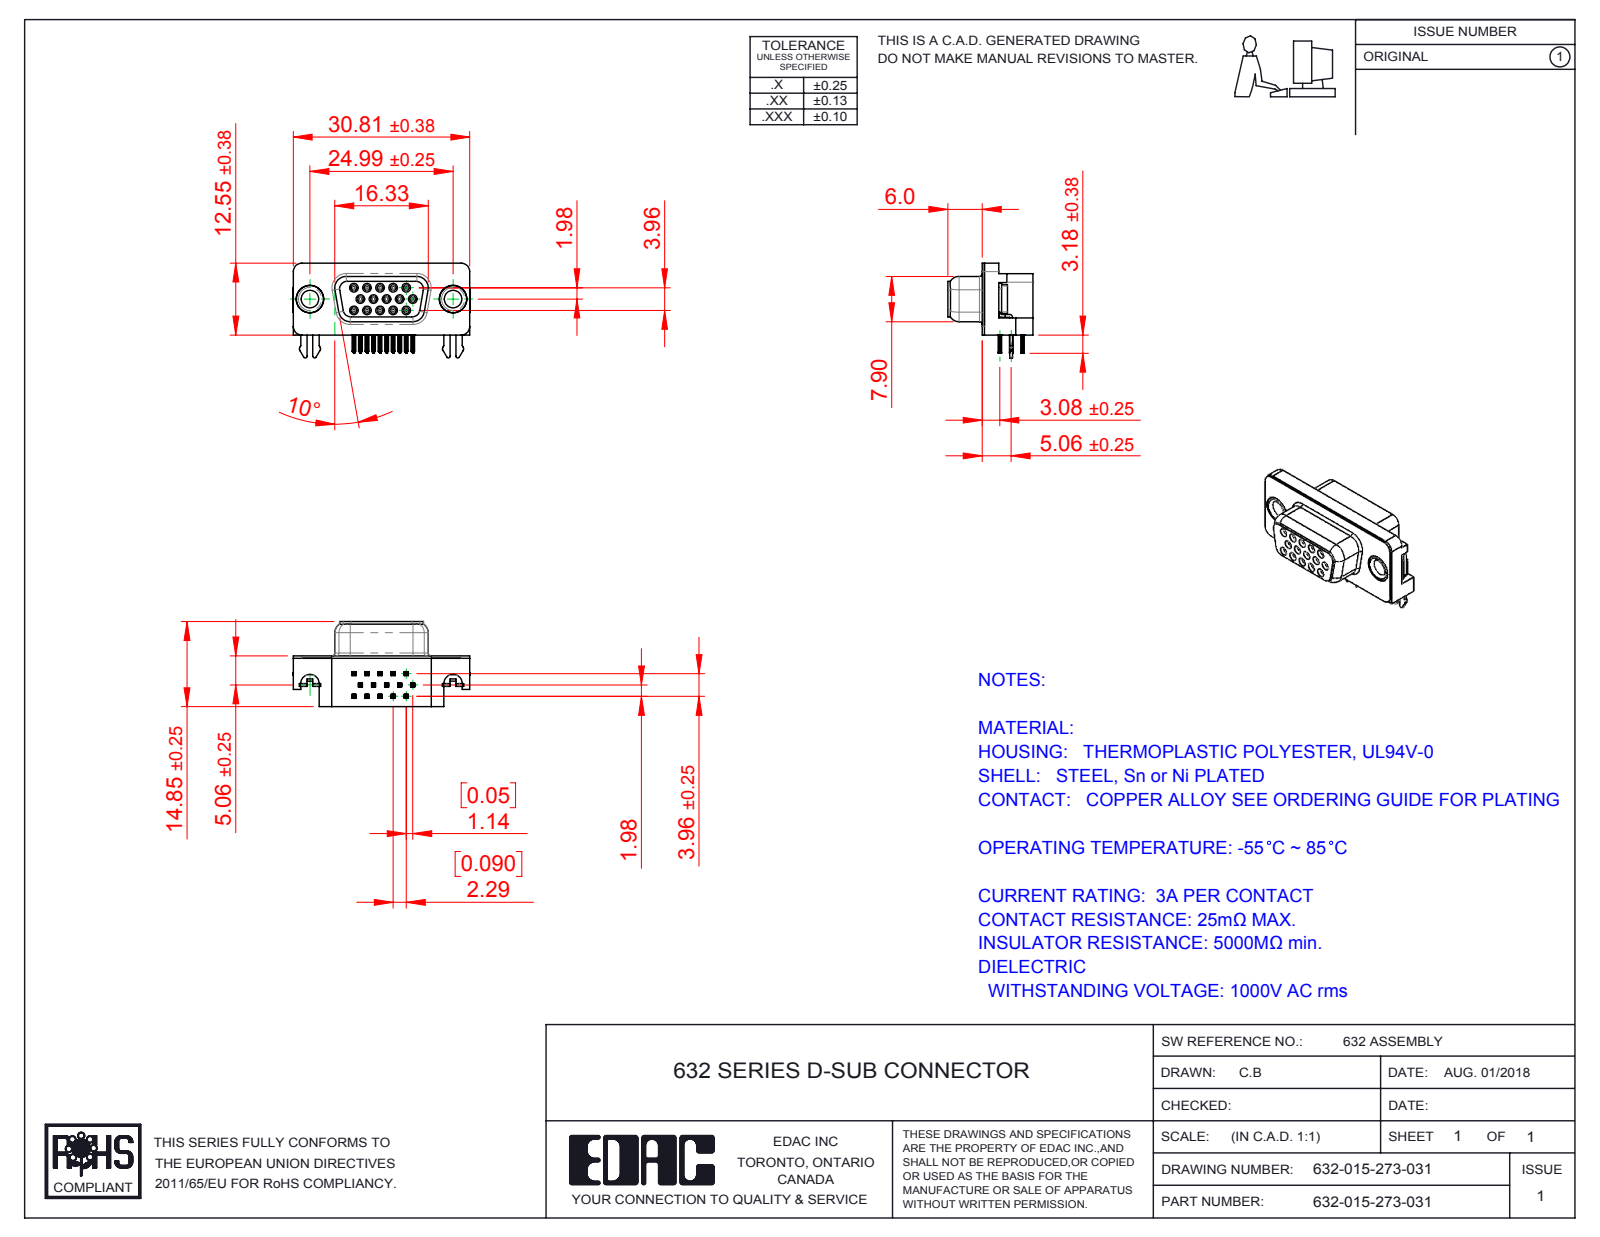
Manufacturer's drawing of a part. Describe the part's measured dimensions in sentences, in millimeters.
The part is named "632 Housing_15 Socket; 632 Shell_9 Socket; 632 Contact Middle; 632 2 Prong Board Lock (+5 more)". Its 3-D file was written by "SolidWorks 2016 (CONFIG_CONTROL_DESIGN)". It is 21 solids with 2298 faces: 990 planar, 594 cylindrical and 714 other. Overall it measures 30.89 by 16.55 by 14.85 millimeters. Its volume is 2 907 cubic millimeters and its surface area 4 991 square millimeters. Round holes: 15 of diameter 0.8, 15 of diameter 0.9, 2 of diameter 3.05, 2 of diameter 4, 2 of diameter 4.8, 2 of diameter 5. Round bosses or shafts: 15 of diameter 1.2, 2 of diameter 4.9, 2 of diameter 4.75, 2 of diameter 3.85. Partial cylindrical surfaces (rounded edges, fillets, slot ends): 120 of radius 0.1, 60 of radius 0.15, 30 of radius 0.35, 15 of radius 0.34, 11 of radius 1, 10 of radius 0.28, 10 of radius 0.5, 8 of radius 0.25. The main face-to-face distances are 0.4, 1.98, 8.45, 8.85, 2.9, 2.5, 5.95, 6.4, 6.7, 7.05. The hole center spacings are 2.28, 2.29, 3.96, 4.57, 6.05, 3.97, 4.58, 6.86.
